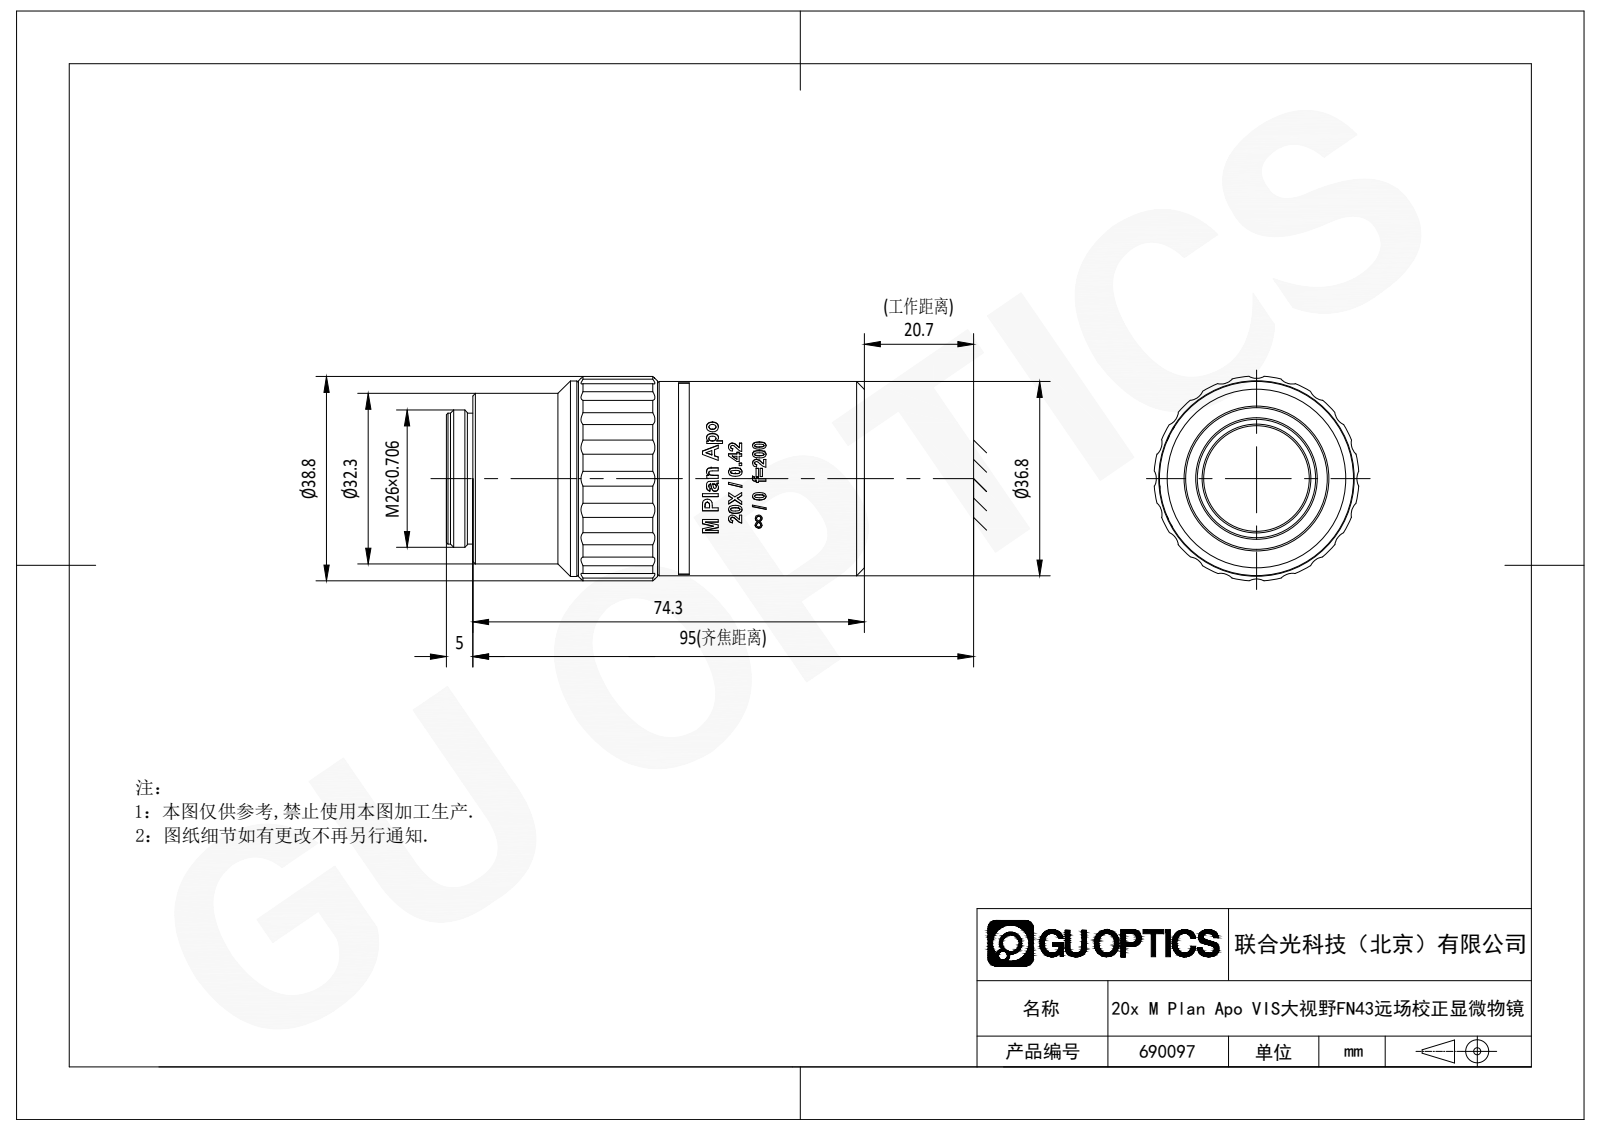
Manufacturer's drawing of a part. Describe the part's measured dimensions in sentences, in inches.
The part is named "690097; 装饰圈.stp". Its 3-D file was written by "SolidWorks 2020 (AUTOMOTIVE_DESIGN)". It is 3 solids with 490 faces: 121 planar, 125 cylindrical and 244 other. Overall it measures 3.118 by 1.524 by 1.524 inches. Its volume is 1.664 cubic inches and its surface area 46.78 square inches. Round holes: 1 of diameter 0.787, 1 of diameter 0.866, 1 of diameter 0.902, 1 of diameter 1.055, 1 of diameter 1.142, 1 of diameter 1.173, 1 of diameter 1.201, 1 of diameter 1.236, 1 of diameter 1.37. Round bosses or shafts: 1 of diameter 1.457, 1 of diameter 1.449, 1 of diameter 1.39, 1 of diameter 1.358, 1 of diameter 1.346, 1 of diameter 1.272, 1 of diameter 1.024, 1 of diameter 0.976. Partial cylindrical surfaces (rounded edges, fillets, slot ends): 20 of radius 0.118, 1 of radius 0.72, 1 of radius 0.764. The main face-to-face distances are 0.039, 0.059, 2.921, 2.823, 2.882, 2.862, 2.134, 2.094, 0.728, 0.787.
